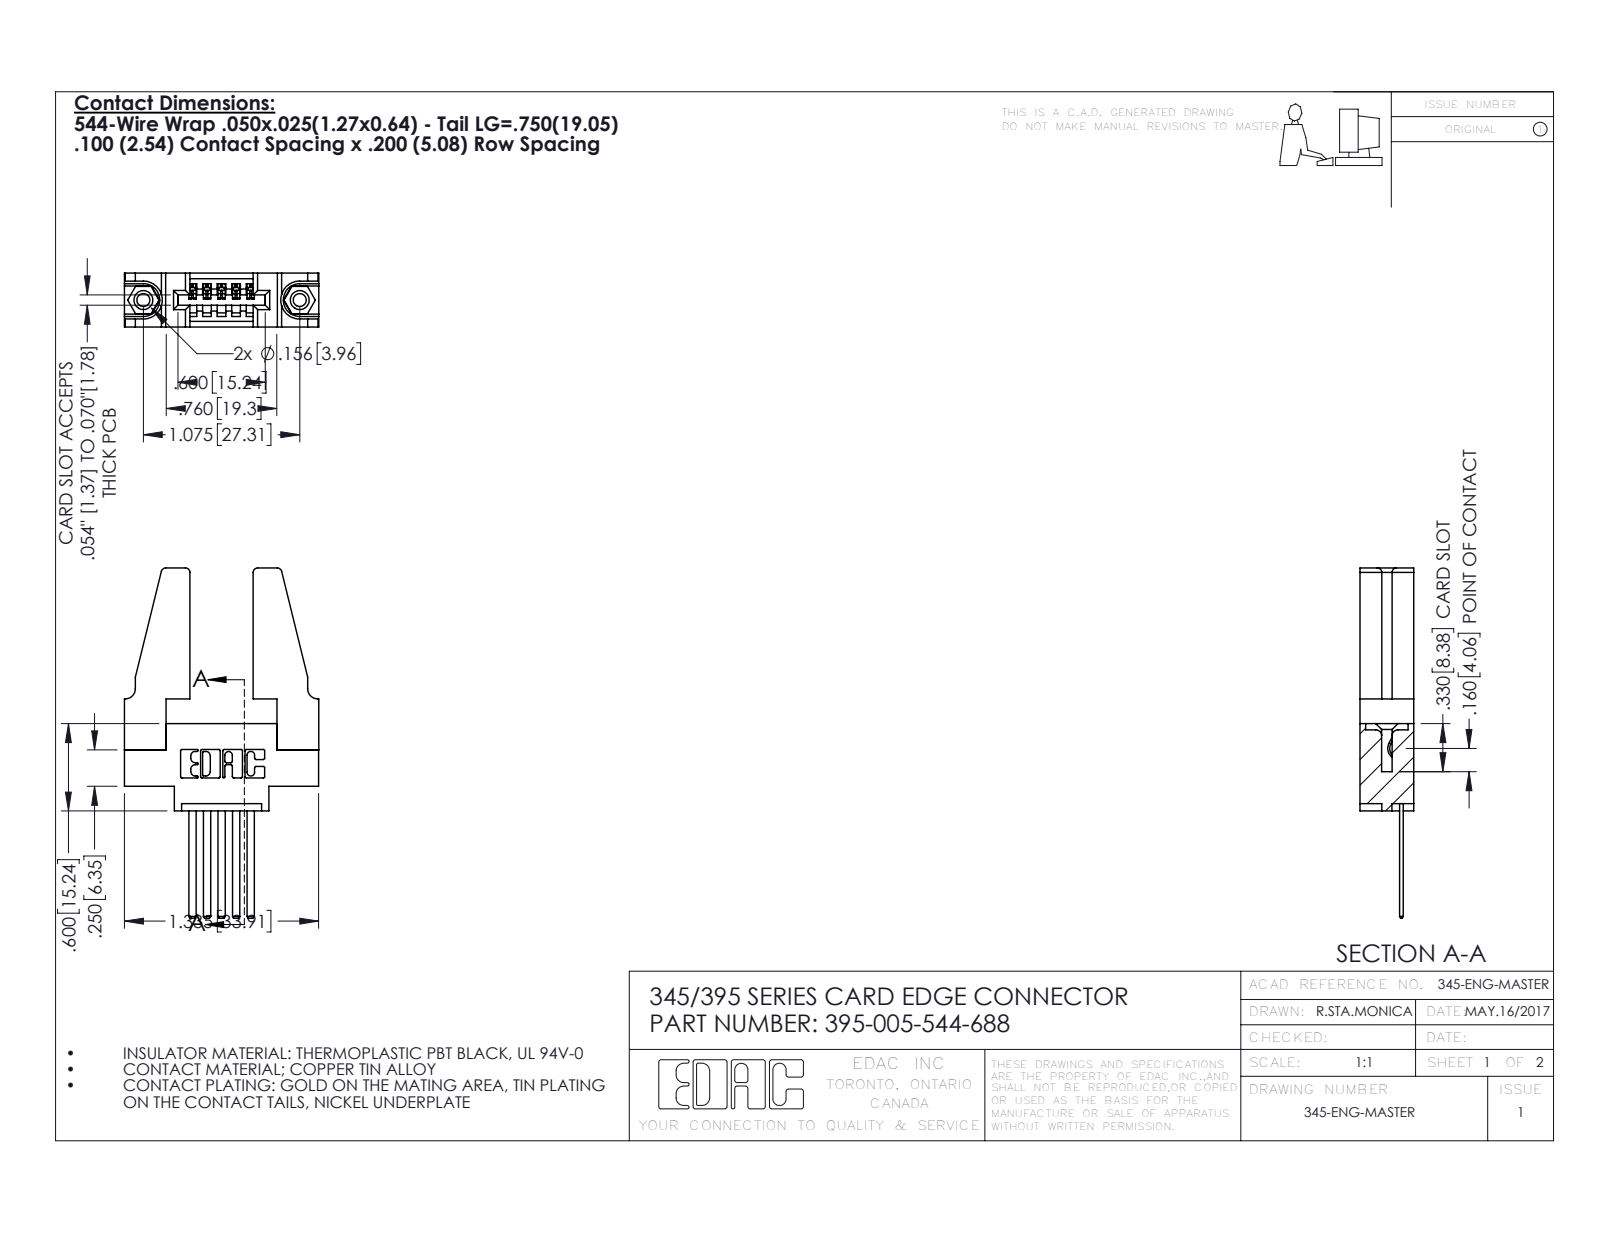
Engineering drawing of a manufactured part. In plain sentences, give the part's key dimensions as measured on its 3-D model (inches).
The part is named "395-005-544-688; 345-292-001_345-293-144; 345-220-078_345-220-088; 345-250-001_345-250-001-102 (+1 more)". Its 3-D file was written by "SolidWorks 2016 (CONFIG_CONTROL_DESIGN)". It is 10 solids with 514 faces: 336 planar, 162 cylindrical and 16 other. Overall it measures 2.407 by 1.336 by 0.37 inches. Its volume is 0.373 cubic inches and its surface area 10.44 square inches. Round holes: 2 of diameter 0.089, 2 of diameter 0.125, 2 of diameter 0.156, 1 of diameter 0.064. Round bosses or shafts: 2 of diameter 0.155. Partial cylindrical surfaces (rounded edges, fillets, slot ends): 22 of radius 0.01, 10 of radius 0.006, 8 of radius 0.03, 6 of radius 0.007, 6 of radius 0.031, 3 of radius 0.026, 2 of radius 0.031, 2 of radius 0.04. The main face-to-face distances are 0.37, 0.072, 0.298, 0.2, 0.098, 0.272, 0.025, 0.148, 0.15, 0.22. The hole center spacings are 0.27, 0.847, 1.075.
